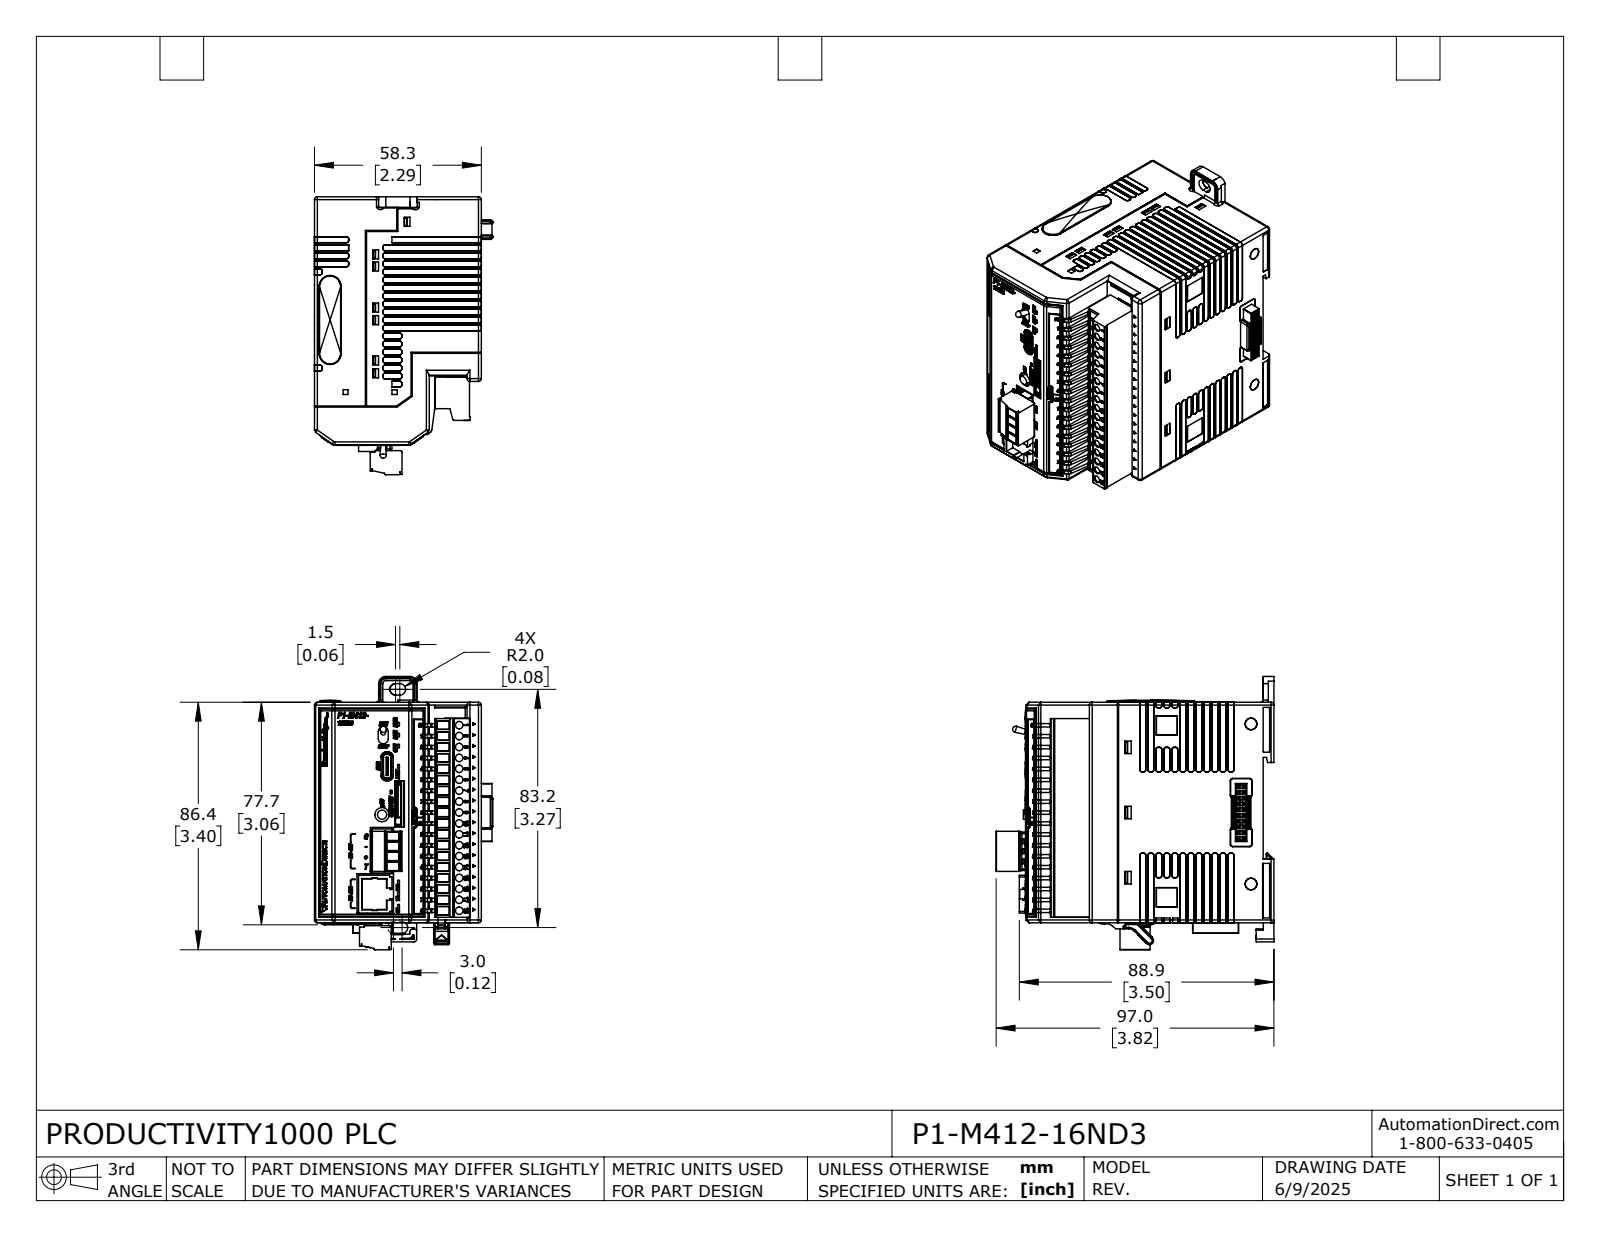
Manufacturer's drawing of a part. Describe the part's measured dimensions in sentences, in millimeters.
The part is named "P1-M412-16ND3". Its 3-D file was written by "SolidWorks 2024 (AUTOMOTIVE_DESIGN)". It is 24 solids with 3659 faces: 2092 planar, 895 cylindrical and 672 other. Overall it measures 93.6 by 91.3 by 62.3 millimeters. Its volume is 34 400 cubic millimeters and its surface area 67 740 square millimeters. Round holes: 1 of diameter 4.9. Round bosses or shafts: 1 of diameter 5.4, 1 of diameter 3.2. Partial cylindrical surfaces (rounded edges, fillets, slot ends): 172 of radius 0.3, 86 of radius 0.2, 49 of radius 0.5, 33 of radius 1, 8 of radius 2, 7 of radius 0.6, 6 of radius 0.1, 4 of radius 0.3. The main face-to-face distances are 56.8, 0.5, 1, 57.8, 76.5, 76.8, 58.3, 58.3, 57.3, 76.7.
